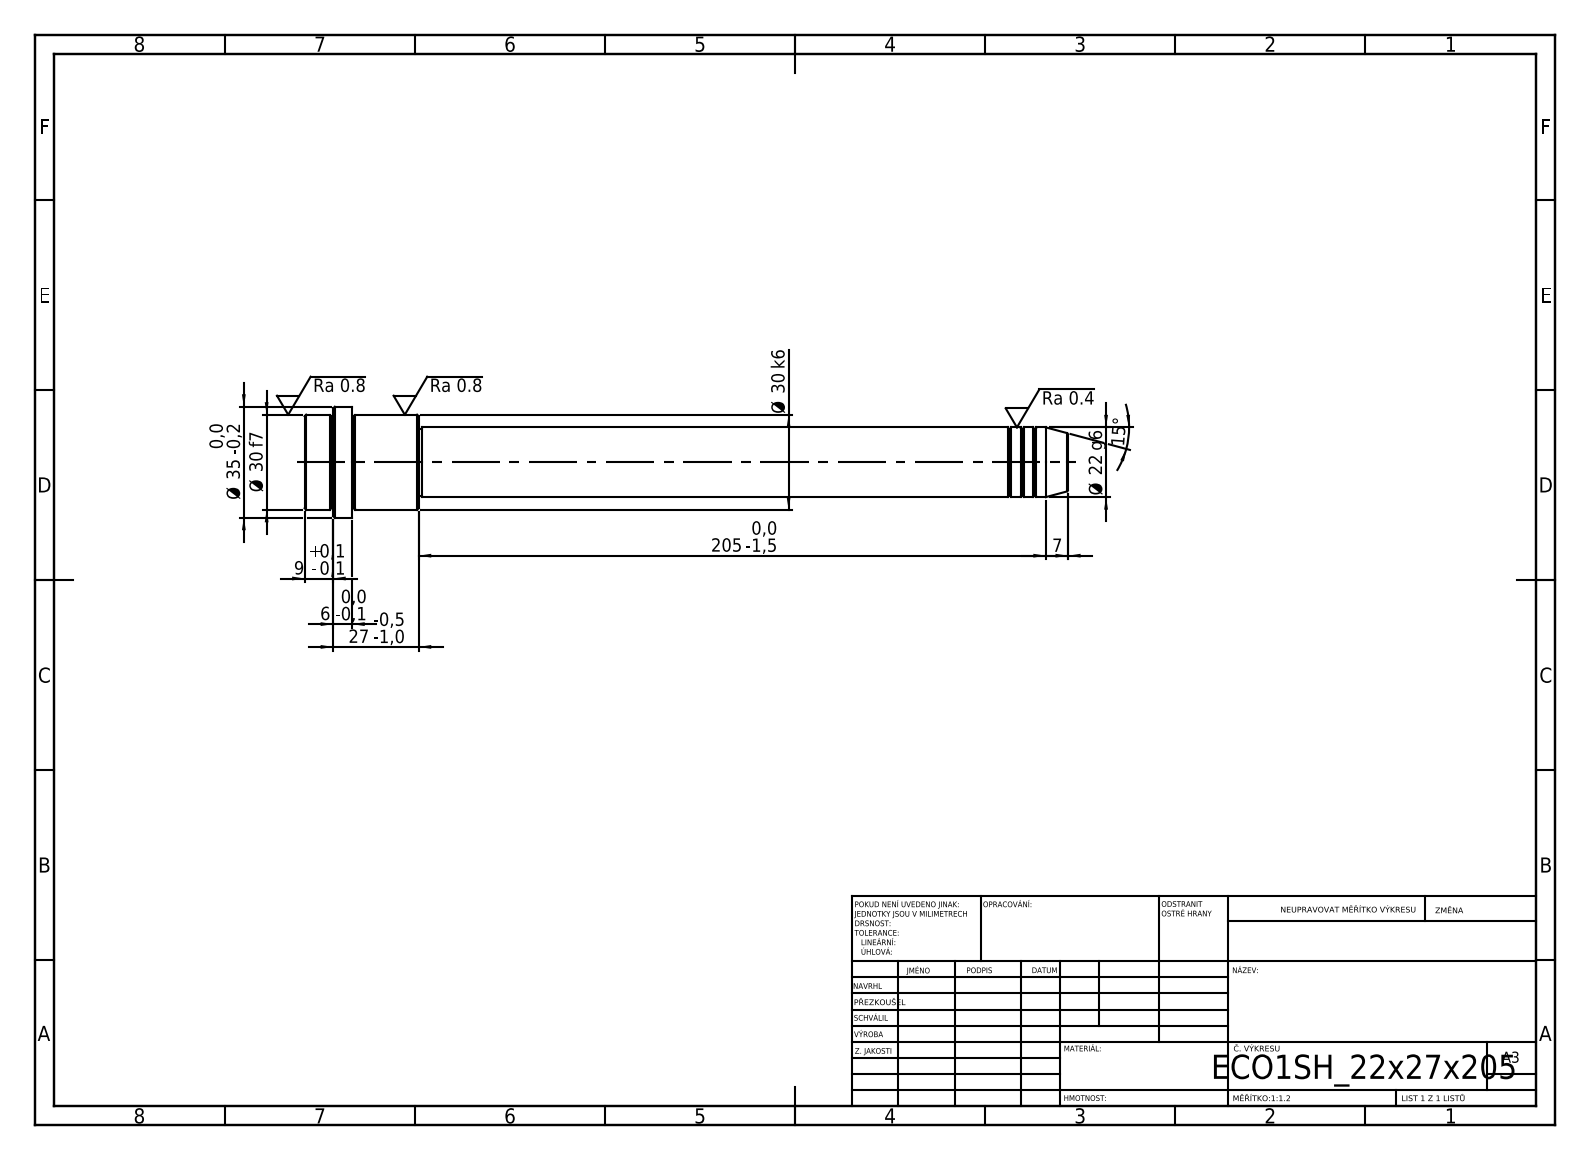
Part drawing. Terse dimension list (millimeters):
written by: SolidWorks 2019 (CONFIG_CONTROL_DESIGN)
unit: mm
bodies: 1 solid, 52 faces (6 planar, 16 cylindrical, 30 other)
size: 241 × 35 × 35
volume: 104 253 mm³; area: 19 615 mm²
bosses: 1× ⌀35, 1× ⌀30, 1× ⌀22, 1× ⌀21
face distances: 36, 21, 15, 205, 226, 241, 232, 27, 6, 9
